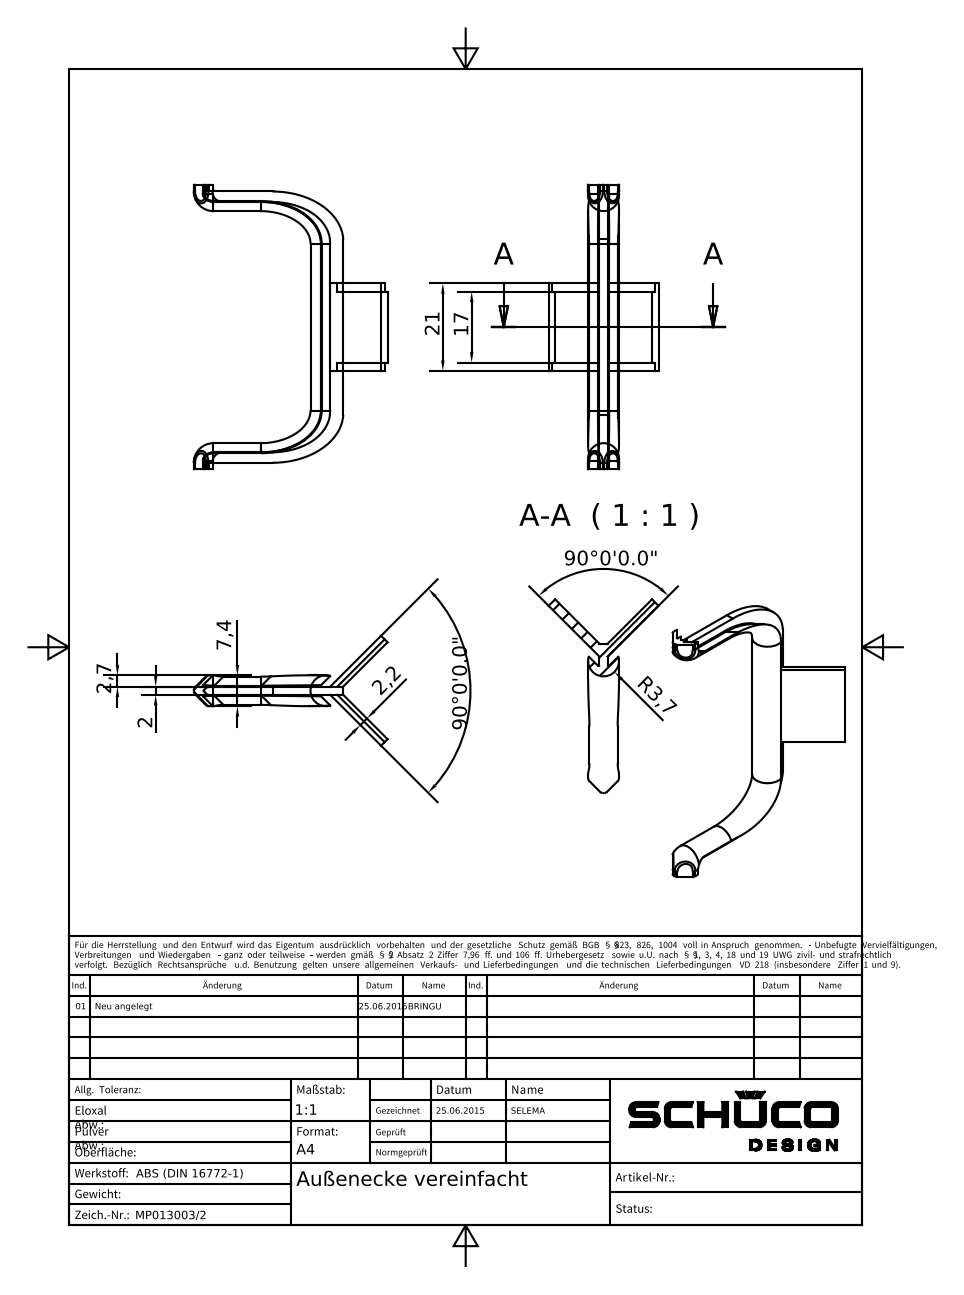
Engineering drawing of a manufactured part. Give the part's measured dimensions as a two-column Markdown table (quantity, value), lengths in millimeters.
| quantity | value |
| --- | --- |
| part name | MP013003 |
| STEP written by | Autodesk Inventor 2024 (AUTOMOTIVE_DESIGN) |
| units | millimeters |
| bodies | 1 solid, 104 faces (45 planar, 37 cylindrical, 22 other) |
| overall size | 68 × 46.42 × 26.32 |
| volume | 3 951 mm³ |
| surface area | 4 637 mm² |
| partial cylindrical surfaces (radius × count) | 0.2 × 9, 1 × 4, 2 × 4, 3.7 × 4, 10 × 4 |
| main face-to-face distances | 2.2, 2, 4, 1.8, 1, 1.2, 3, 16.41, 17.41, 18.61 |
